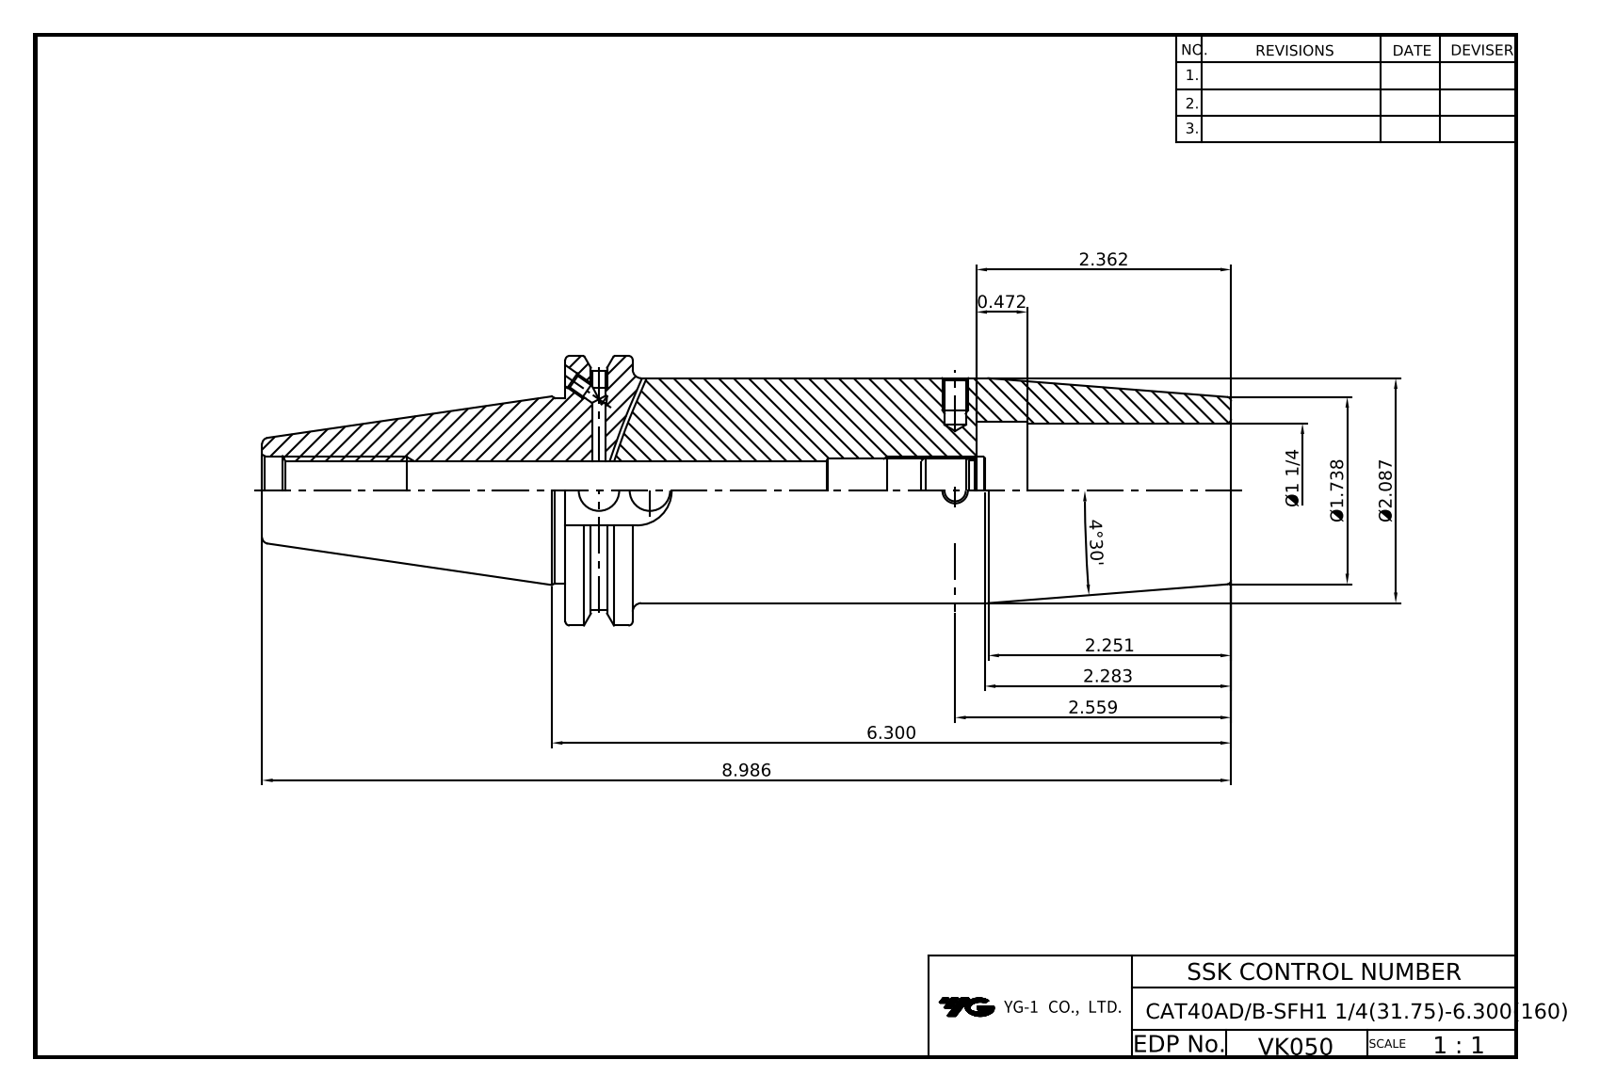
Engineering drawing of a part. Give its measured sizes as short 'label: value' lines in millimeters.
name: LO-CAT40ADB-SFH31.75-160
written by: Autodesk Inventor 2022 (AUTOMOTIVE_DESIGN)
unit: mm
bodies: 1 solid, 87 faces (34 planar, 31 cylindrical, 22 other)
size: 228.25 × 63.5 × 61.09
volume: 330 501 mm³; area: 52 339 mm²
holes: 4× ⌀3.24, 2× ⌀4, 2× ⌀4.2, 1× ⌀9.53, 1× ⌀13, 1× ⌀13.39, 1× ⌀14.92, 1× ⌀16.3, 1× ⌀31.75, 1× ⌀32.95
bosses: 1× ⌀63.5, 1× ⌀53, 1× ⌀43.6
rounds: 1× R8.19, 1× R28.15
face distances: 96.83, 156.83, 60, 15.88, 80.95, 140.95, 47.6, 16.38, 71.42, 87.3
